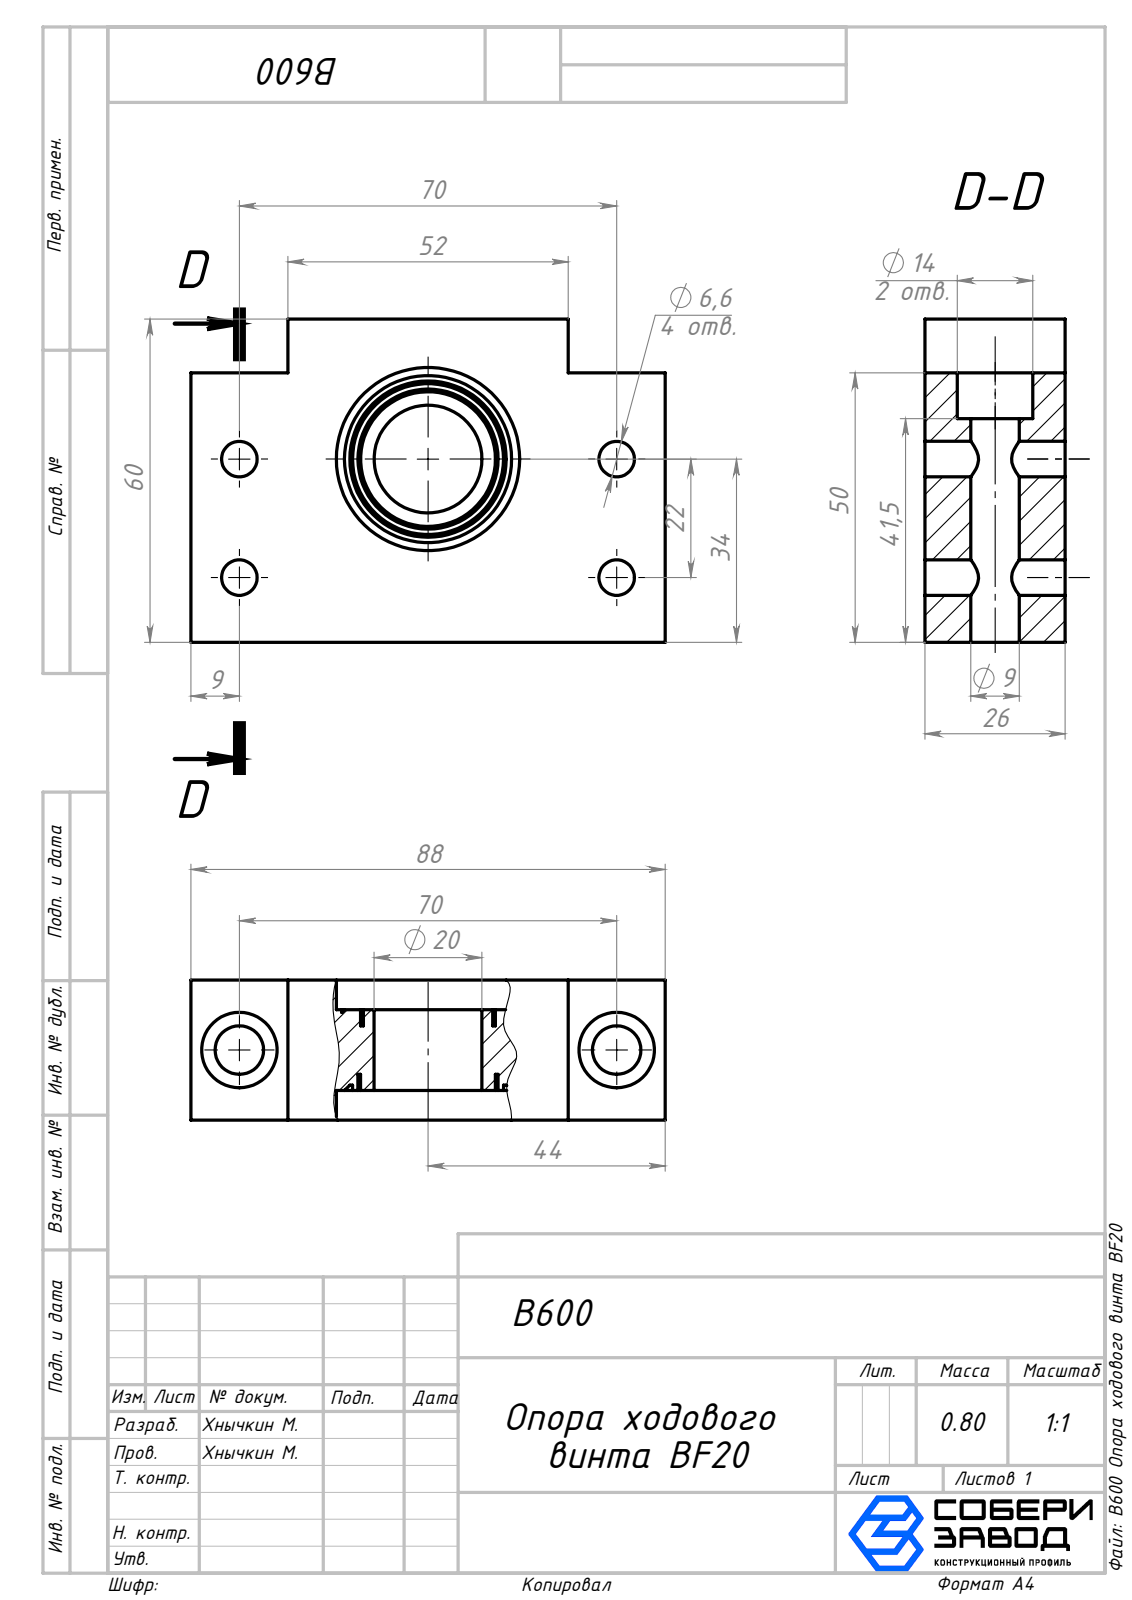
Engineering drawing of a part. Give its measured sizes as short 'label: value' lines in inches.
name: B600 Опора ходового винта BF20
written by: SolidWorks 2026 (AUTOMOTIVE_DESIGN)
unit: in
bodies: 1 solid, 67 faces (21 planar, 42 cylindrical, 4 other)
size: 3.465 × 2.362 × 1.024
volume: 6.259 in³; area: 37.13 in²
holes: 4× ⌀0.26, 2× ⌀0.354, 2× ⌀0.551, 1× ⌀0.787, 1× ⌀0.984, 1× ⌀1.024, 1× ⌀1.26, 1× ⌀1.339
bosses: 1× ⌀1.102, 1× ⌀0.945
face distances: 1.024, 2.362, 3.465, 0.217, 0.807, 1.969, 0.394, 0.709, 2.756, 0.591
hole spacings: 2.756, 0.866, 1.378, 1.628, 2.889
